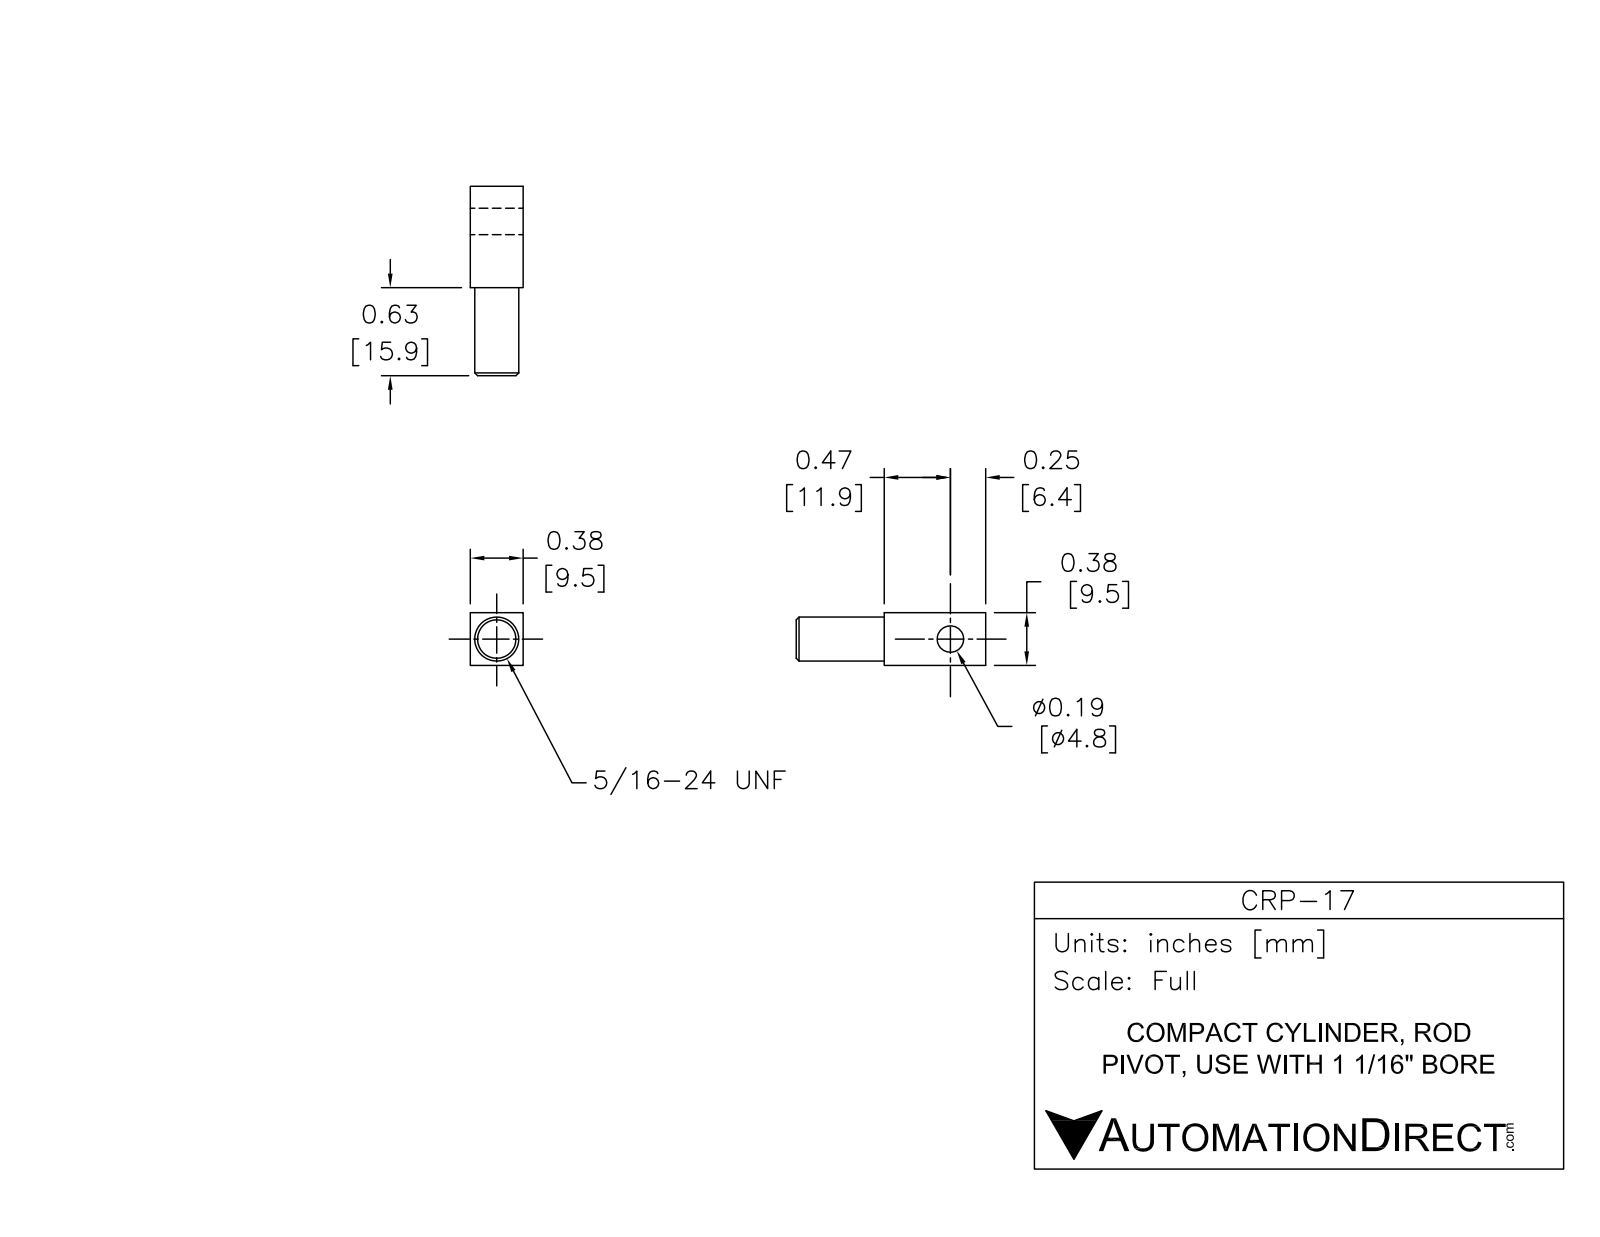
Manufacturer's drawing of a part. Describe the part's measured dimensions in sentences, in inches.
The part is named "CRP-17; CRP-17_bushing; CRP-17_nut; CRP-17_bracket". Its 3-D file was written by "SolidWorks 2014 (AUTOMOTIVE_DESIGN)". It is 3 solids with 45 faces: 17 planar, 10 cylindrical and 18 other. Overall it measures 1.35 by 0.577 by 0.5 inches. Its volume is 0.171 cubic inches and its surface area 3.531 square inches. Round holes: 1 of diameter 0.19, 1 of diameter 0.252, 1 of diameter 0.267. Round bosses or shafts: 1 of diameter 0.313. The main face-to-face distances are 0.38, 0.5, 0.44, 0.72, 0.19, 0.91, 0.06, 0.63, 1.35.
